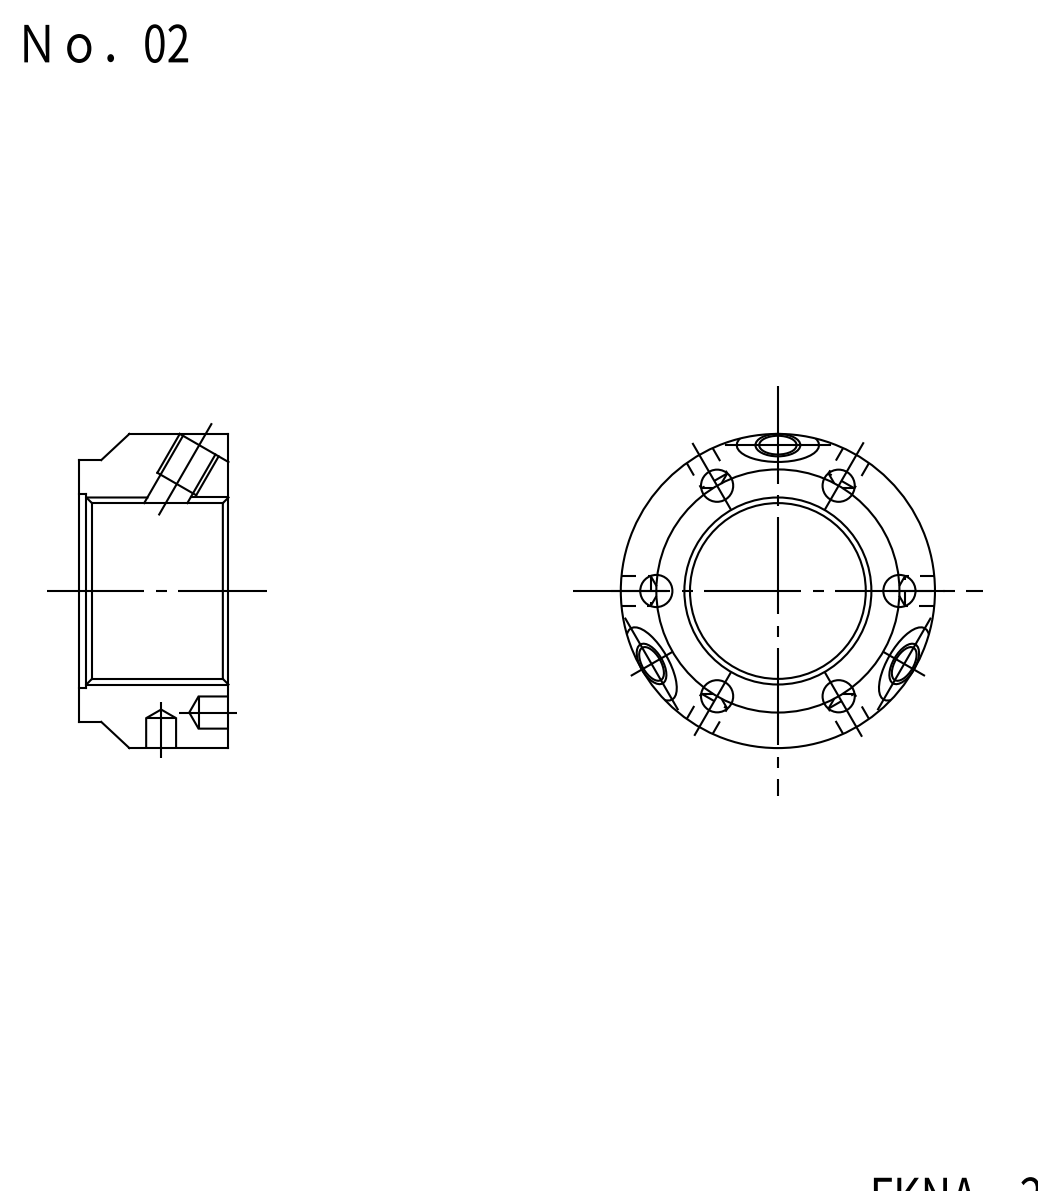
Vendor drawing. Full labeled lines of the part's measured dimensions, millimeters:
Part name (STEP PRODUCT): FKD FKNA25
STEP written by: Autodesk Inventor LT (CONFIG_CONTROL_DESIGN)
Units: millimetres
Bodies: 1 solid, 44 faces (6 planar, 25 cylindrical, 13 other)
Overall size (bounding box): 42 × 42 × 20
Volume: 15 326 mm³ · Surface area: 6 789 mm²
Round holes (diameter × count): ⌀4.3 ×6, ⌀4 ×3, ⌀6.1 ×3, ⌀4.92 ×2, ⌀4.92 ×1, ⌀25 ×1, ⌀26 ×1
Round bosses / shafts (diameter × count): ⌀42 ×1, ⌀35 ×1
Partial cylindrical surfaces — rounded edges, fillets, slot ends (radius × count): R20 ×3
Main face-to-face distances: 20, 1.5, 18.5
Hole centre spacings: 16.25, 16.24, 28.14, 28.15, 32.5, 16.26, 32.49
